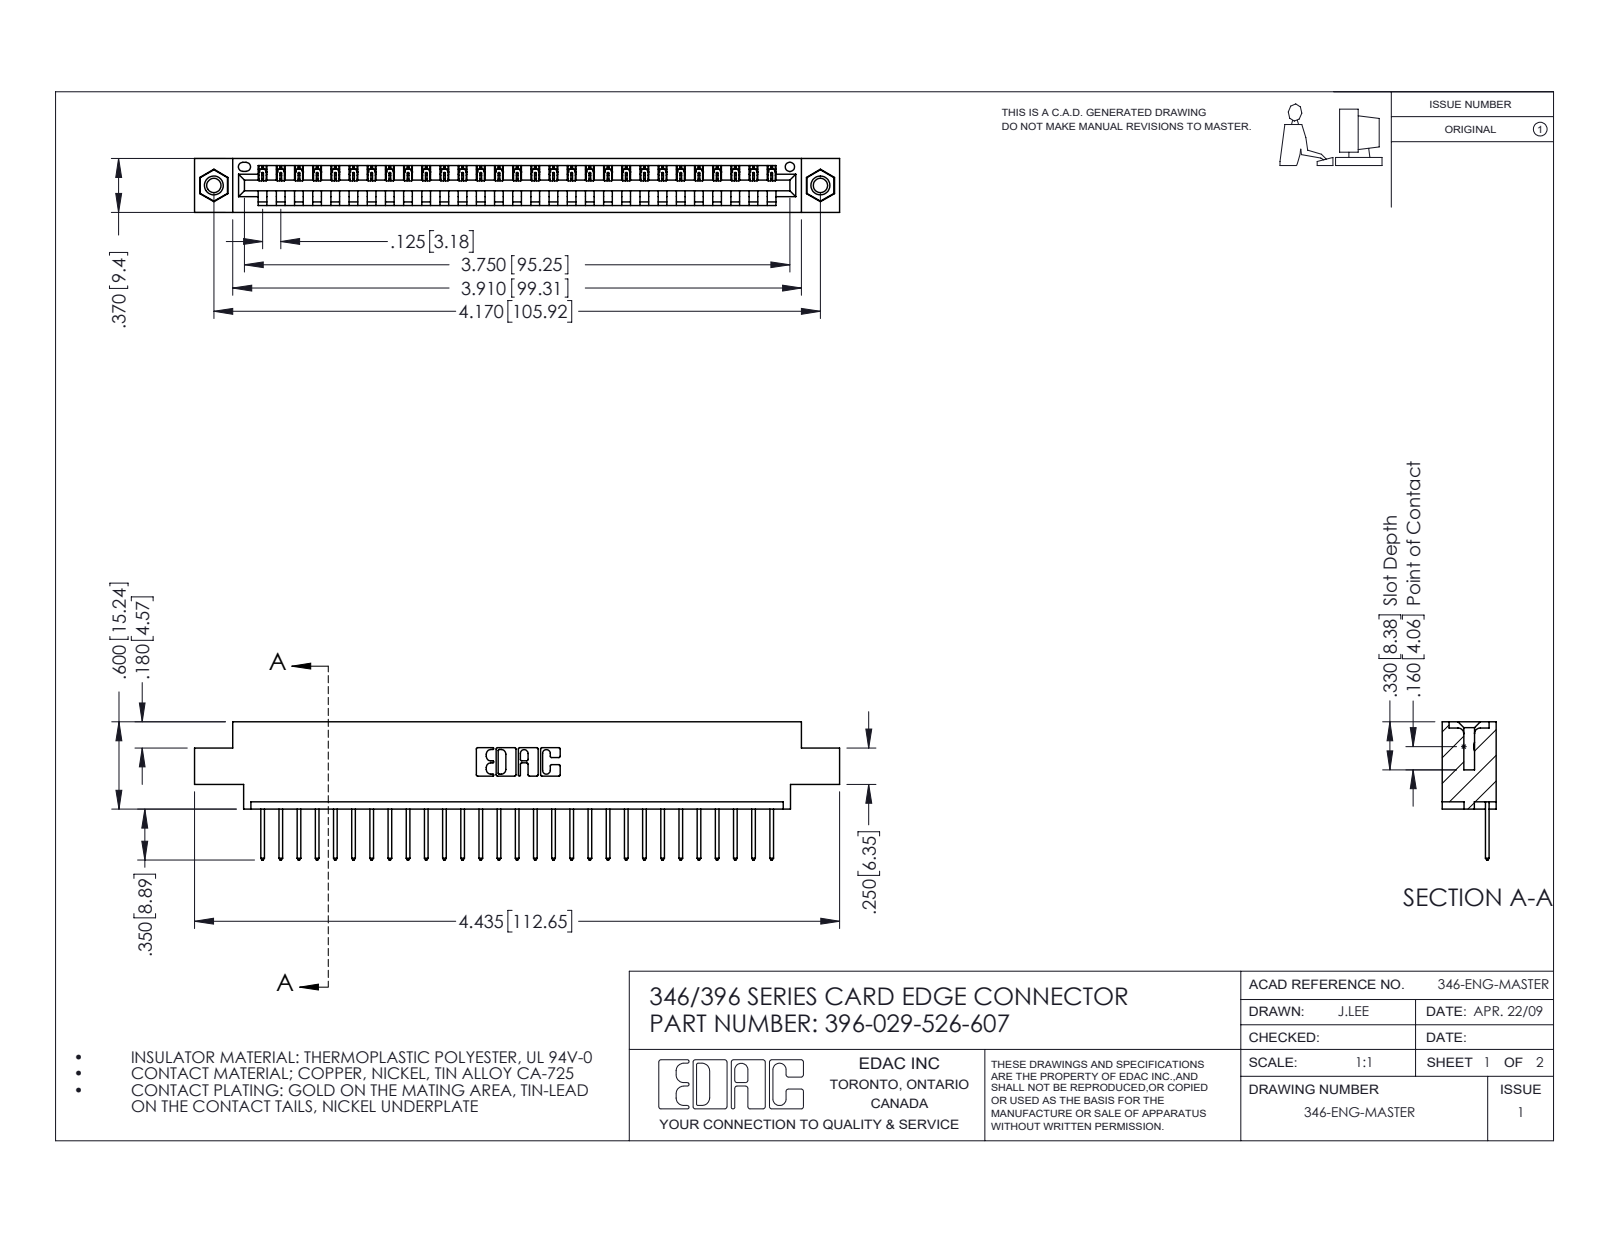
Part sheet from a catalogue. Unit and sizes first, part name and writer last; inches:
Units: inches
Overall size (bounding box): 4.435 × 0.95 × 0.37
Round holes (diameter × count): ⌀0.098 ×2, ⌀0.125 ×2, ⌀0.156 ×2, ⌀0.064 ×1
Round bosses / shafts (diameter × count): ⌀0.155 ×2
Partial cylindrical surfaces — rounded edges, fillets, slot ends (radius × count): R0.006 ×58, R0.01 ×58, R0.01 ×22, R0.007 ×6, R0.031 ×6, R0.026 ×3, R0.031 ×2, R0.04 ×2
Main face-to-face distances: 0.048, 0.322, 0.37, 0.25, 0.072, 0.298, 0.025, 0.222, 0.148, 0.1
Hole centre spacings: 0.246, 3.962, 4.17
Volume: 0.641 in³ · Surface area: 20.39 in²
Bodies: 32 solids, 1868 faces (1272 planar, 580 cylindrical, 16 other)
Part name (STEP PRODUCT): 345-250-001_345-250-005-103; 346 Part_0.170 Offset - 0.156 Dia-TI; 345-292-001_345-293-126; 396-029-526-607
STEP written by: SolidWorks 2016 (CONFIG_CONTROL_DESIGN)
